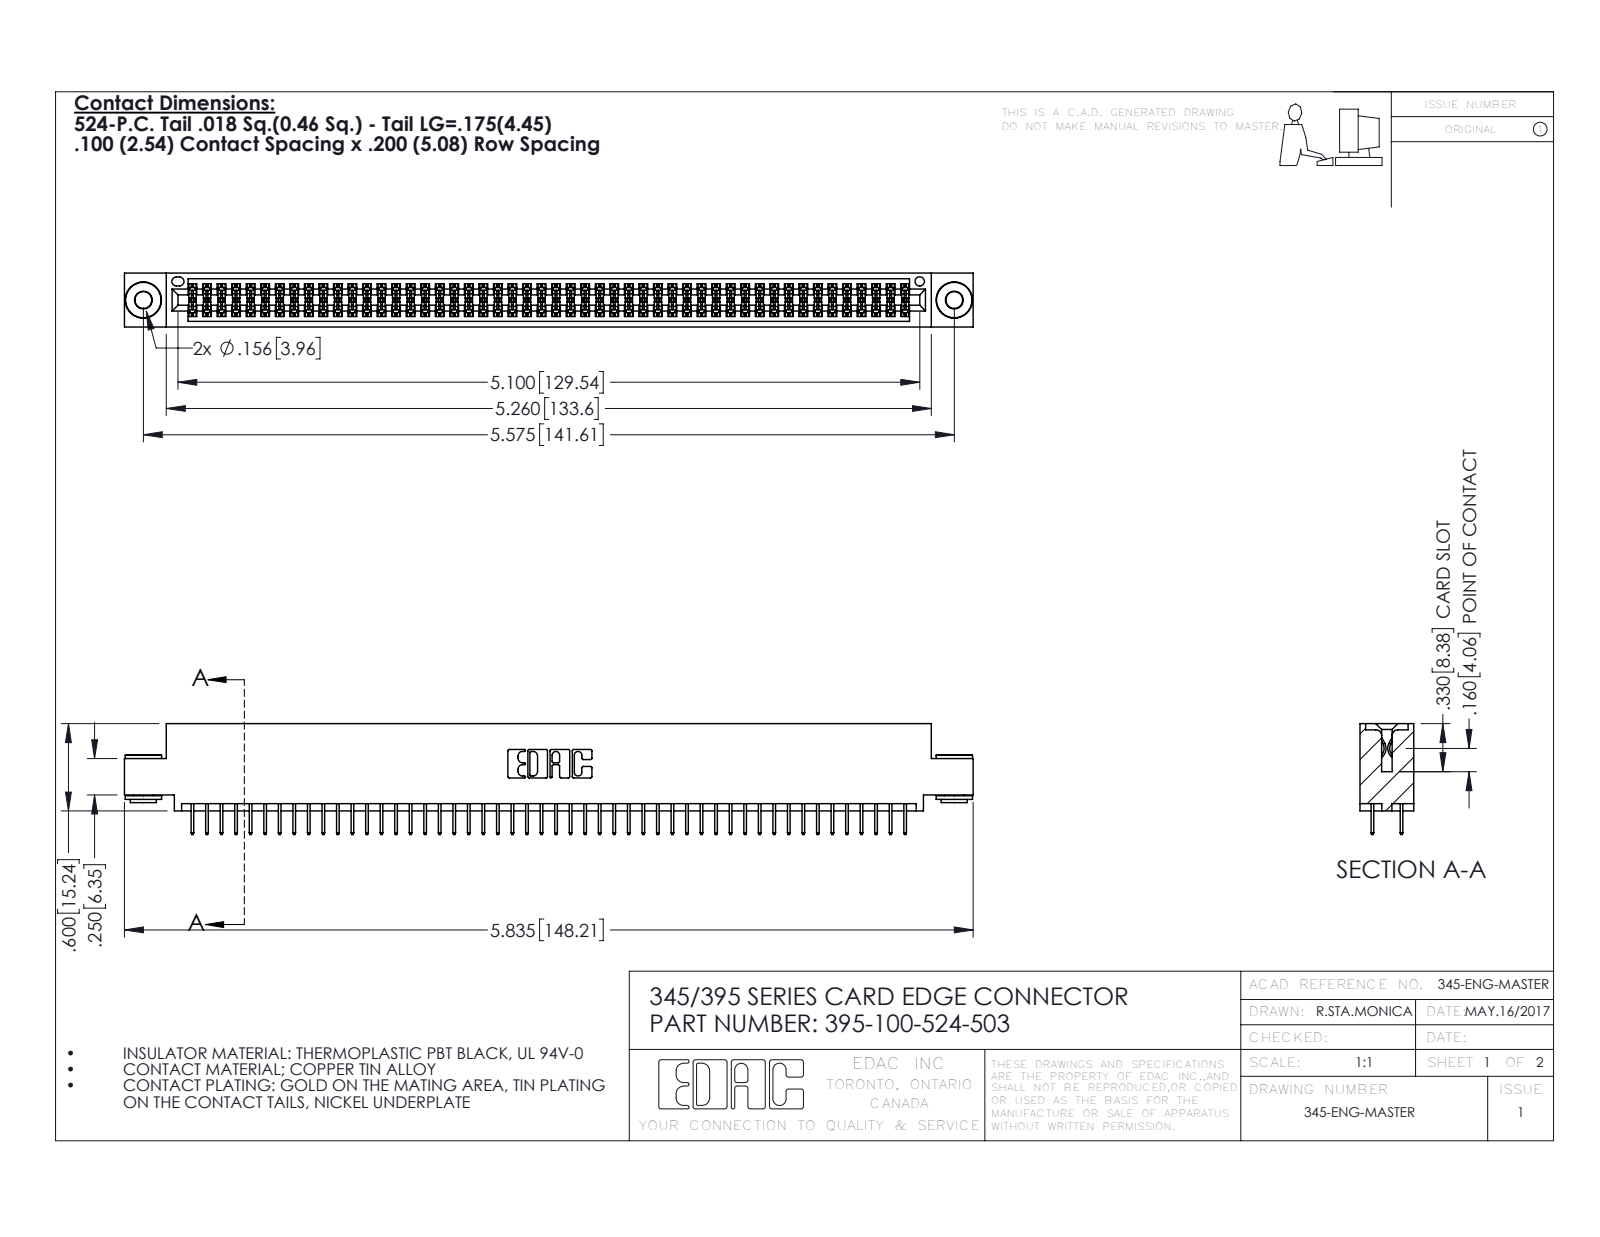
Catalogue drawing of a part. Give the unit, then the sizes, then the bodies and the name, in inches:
Units: inches
Overall size (bounding box): 5.835 × 0.762 × 0.37
Round holes (diameter × count): ⌀0.116 ×2, ⌀0.156 ×2, ⌀0.064 ×1
Round bosses / shafts (diameter × count): ⌀0.25 ×2, ⌀0.18 ×2, ⌀0.136 ×2
Partial cylindrical surfaces — rounded edges, fillets, slot ends (radius × count): R0.006 ×150, R0.01 ×22, R0.007 ×6, R0.031 ×6, R0.026 ×3, R0.014 ×2, R0.019 ×2, R0.022 ×2
Main face-to-face distances: 0.072, 0.298, 0.2, 0.37, 0.025, 0.098, 0.272, 0.225, 0.072, 0.175
Hole centre spacings: 0.27, 5.339, 5.575
Volume: 0.871 in³ · Surface area: 32.77 in²
Bodies: 103 solids, 5568 faces (3994 planar, 1566 cylindrical, 8 other)
Part name (STEP PRODUCT): 345-292-001_345-293-124; 395-100-524-503; 345-250-002_345-250-002-102; 345 Part_0.110 Offset - 0.156 Dia-TH
STEP written by: SolidWorks 2016 (CONFIG_CONTROL_DESIGN)
